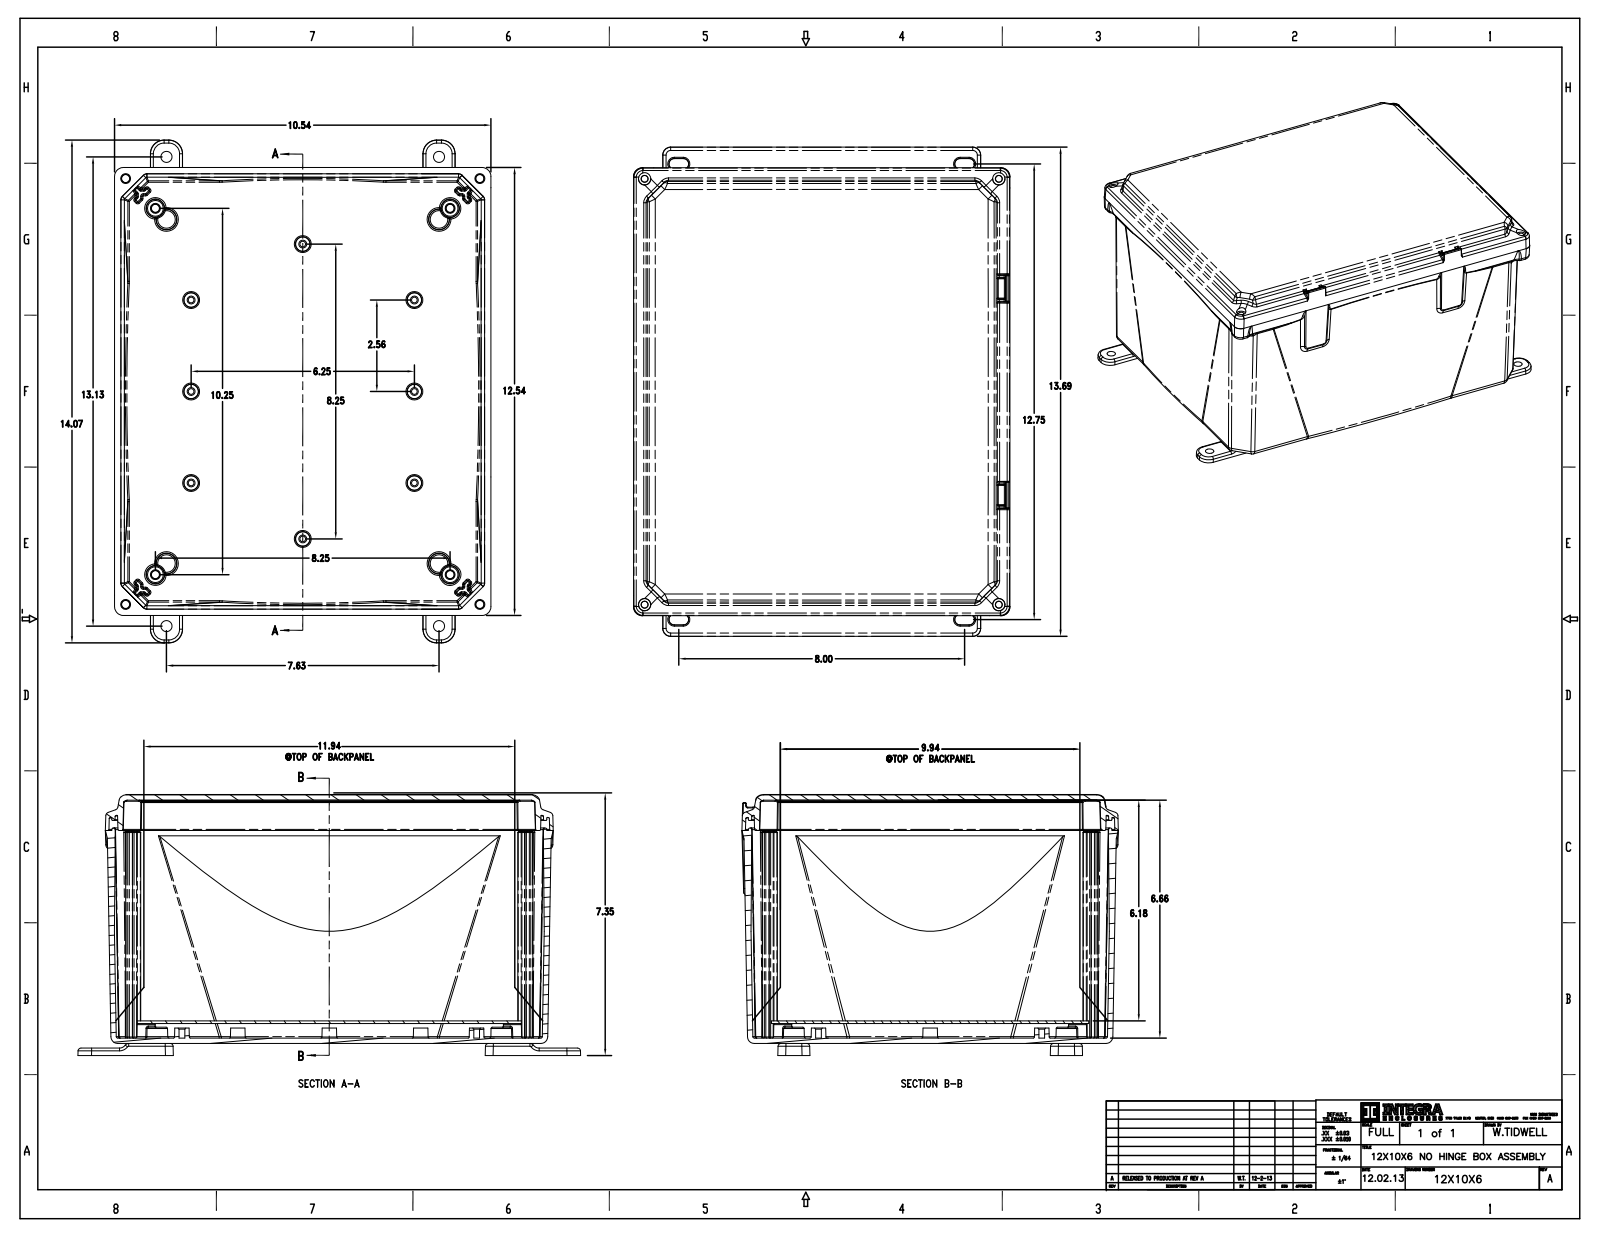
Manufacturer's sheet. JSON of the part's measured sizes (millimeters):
{"part_name": "1210600; 1210640; 12X10_BACKPANEL; 10INCH-MOUNTING-FLANGE (+1 more)", "step_written_by": "CREO PARAMETRIC BY PTC INC, 2016050 (CONFIG_CONTROL_DESIGN)", "units": "millimeters", "bodies": {"solids": 5, "faces": 2960, "planar": 602, "cylindrical": 1132, "other": 1226}, "overall_size": [347.7, 267.6, 186.7], "volume_mm3": 1704000, "surface_area_mm2": 964500, "round_holes": [[4.1, 8], [6.4, 4]], "partial_cylinders_radius": [[0.8, 432], [0.5, 152], [2.3, 36], [2.5, 28], [2, 26], [5.1, 24], [1, 21], [0.6, 16]], "face_to_face_distances": [3.8, 14.1, 10.3, 16, 12.2, 1.9, 12.4, 3, 147.6, 151.4], "hole_center_spacings": [65, 69.9, 88.8, 107.8, 131.4, 132.6, 171.6, 187.4]}
